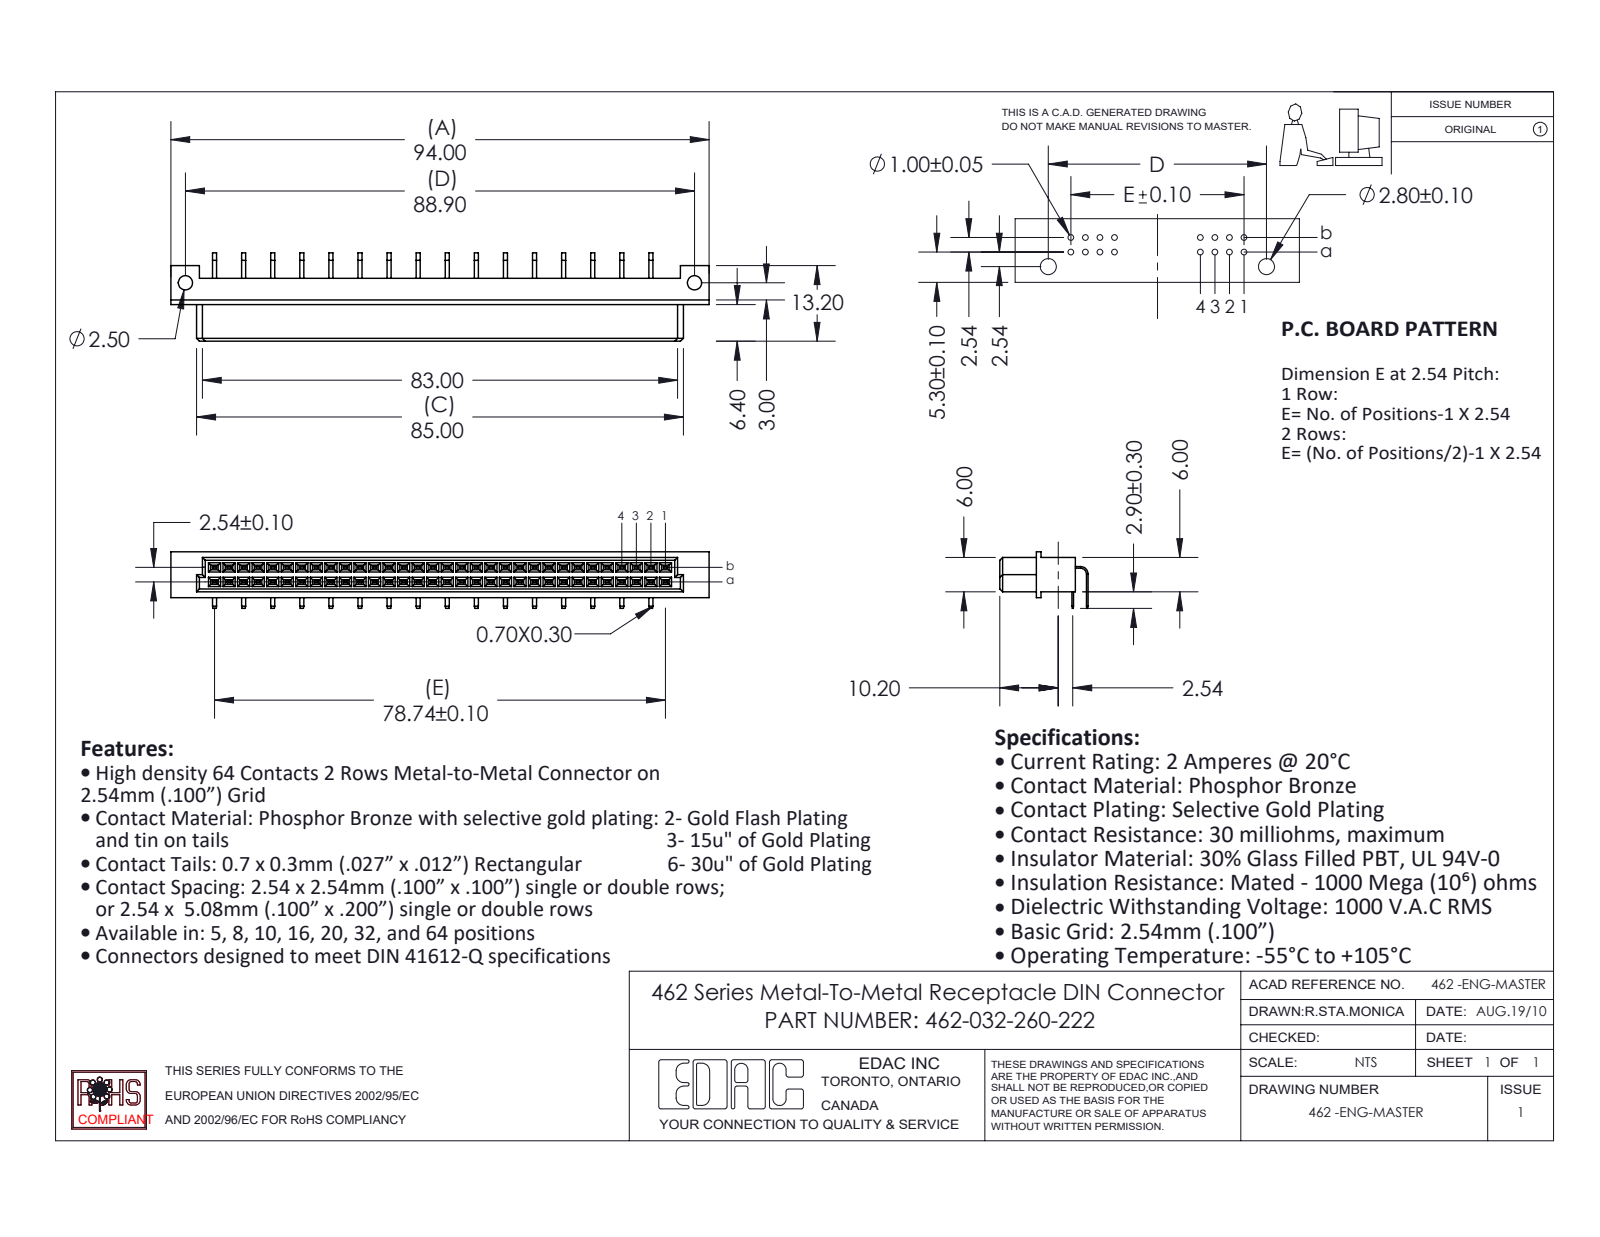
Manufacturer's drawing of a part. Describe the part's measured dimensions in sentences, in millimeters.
The part is named "462-290-2; 462 Part_64; 462-290-1; 462-032-260-222". Its 3-D file was written by "SolidWorks 2020 (CONFIG_CONTROL_DESIGN)". It is 33 solids with 1315 faces: 1247 planar, 68 cylindrical and 0 other. Overall it measures 94 by 15.43 by 9.9 millimeters. Its volume is 5 574 cubic millimeters and its surface area 6 704 square millimeters. Round holes: 2 of diameter 2.5. Partial cylindrical surfaces (rounded edges, fillets, slot ends): 2 of radius 1.02, 2 of radius 1.32. The main face-to-face distances are 2.54, 6, 0.81, 0.55, 1.58, 1.88, 4.12, 4.42, 0.56, 4.6. The hole center spacings are 88.9.
